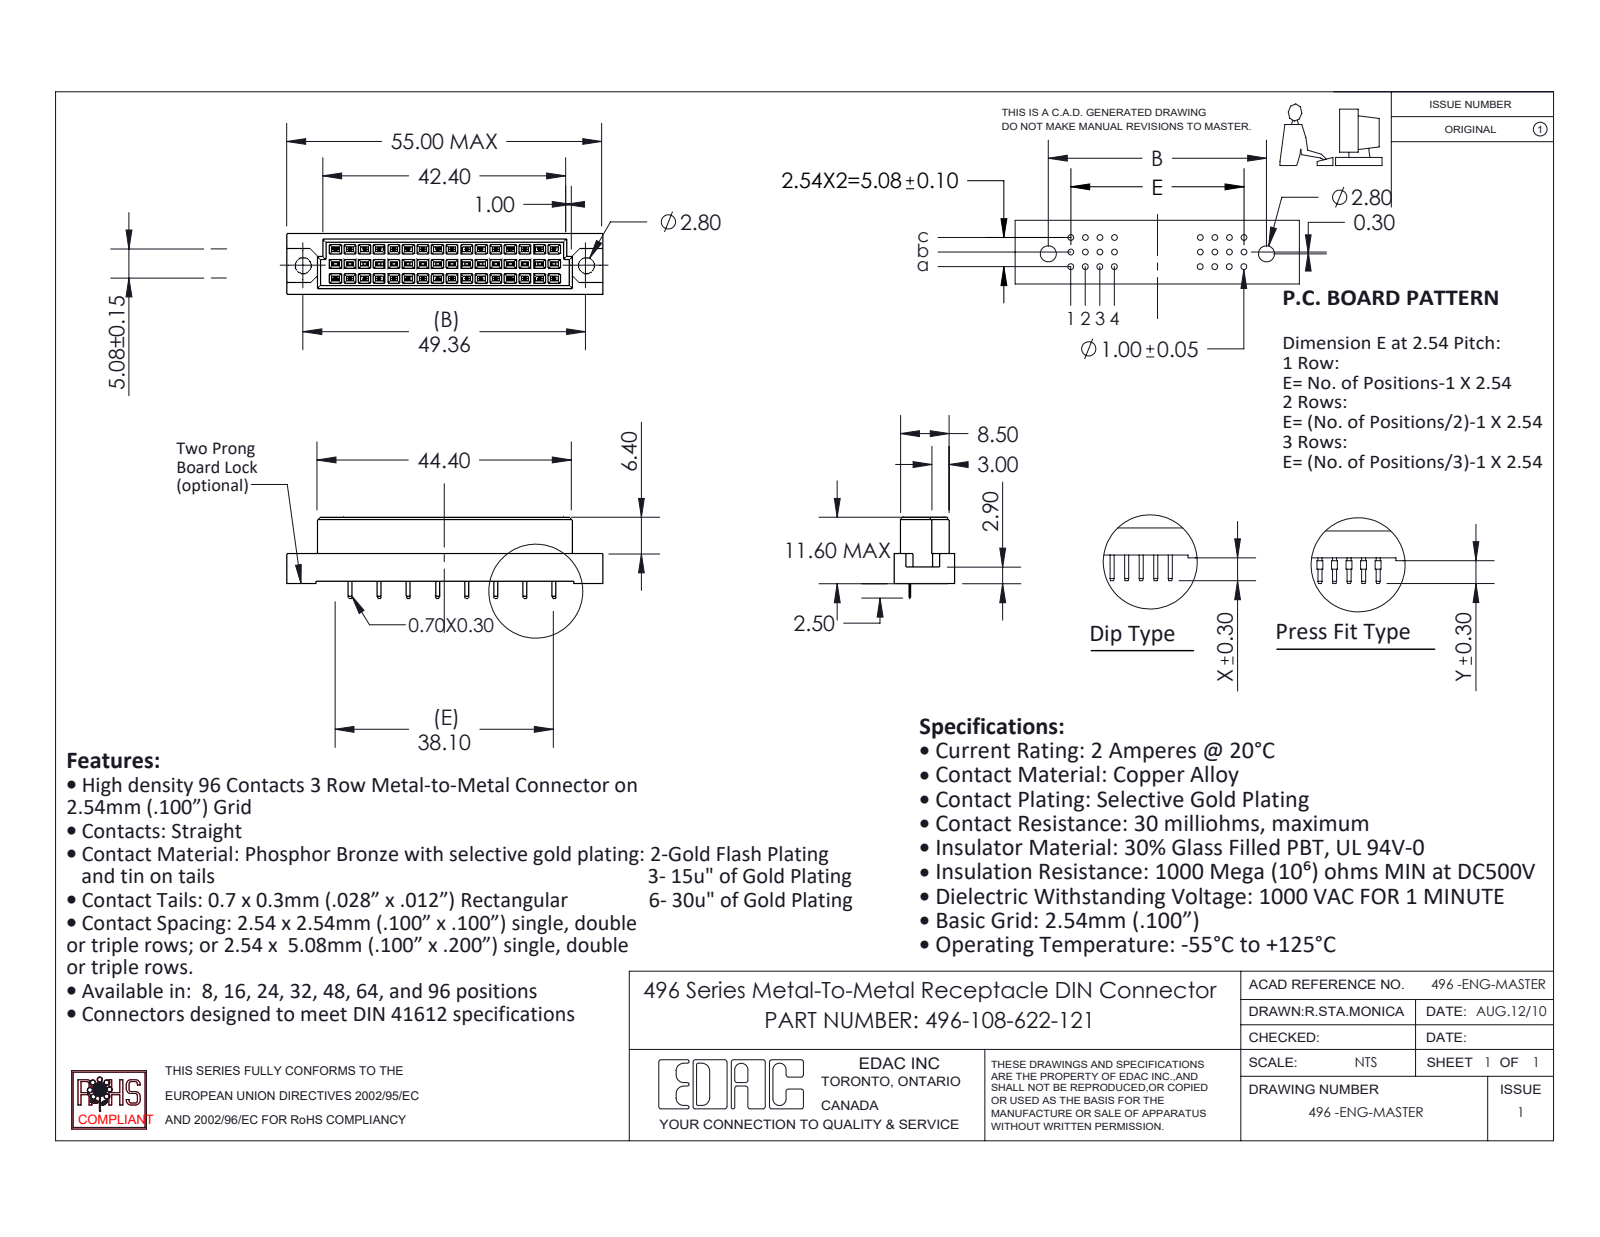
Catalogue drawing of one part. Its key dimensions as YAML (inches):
part_name: "496-108-622-121; 496-290_22; 496 Part_48"
step_written_by: "SolidWorks 2020 (CONFIG_CONTROL_DESIGN)"
units: inches
bodies: {solids: 9, faces: 746, planar: 742, cylindrical: 4, other: 0}
overall_size: [2.165, 0.555, 0.417]
volume: 0.281
surface_area: 6.716
round_holes:
  - {diameter: 0.11, count: 2}
face_to_face_distances: [0.1, 0.2, 0.041, 0.376, 0.032, 0.417, 0.132, 0.068, 0.335, 0.022]
hole_center_spacings: [1.943]
